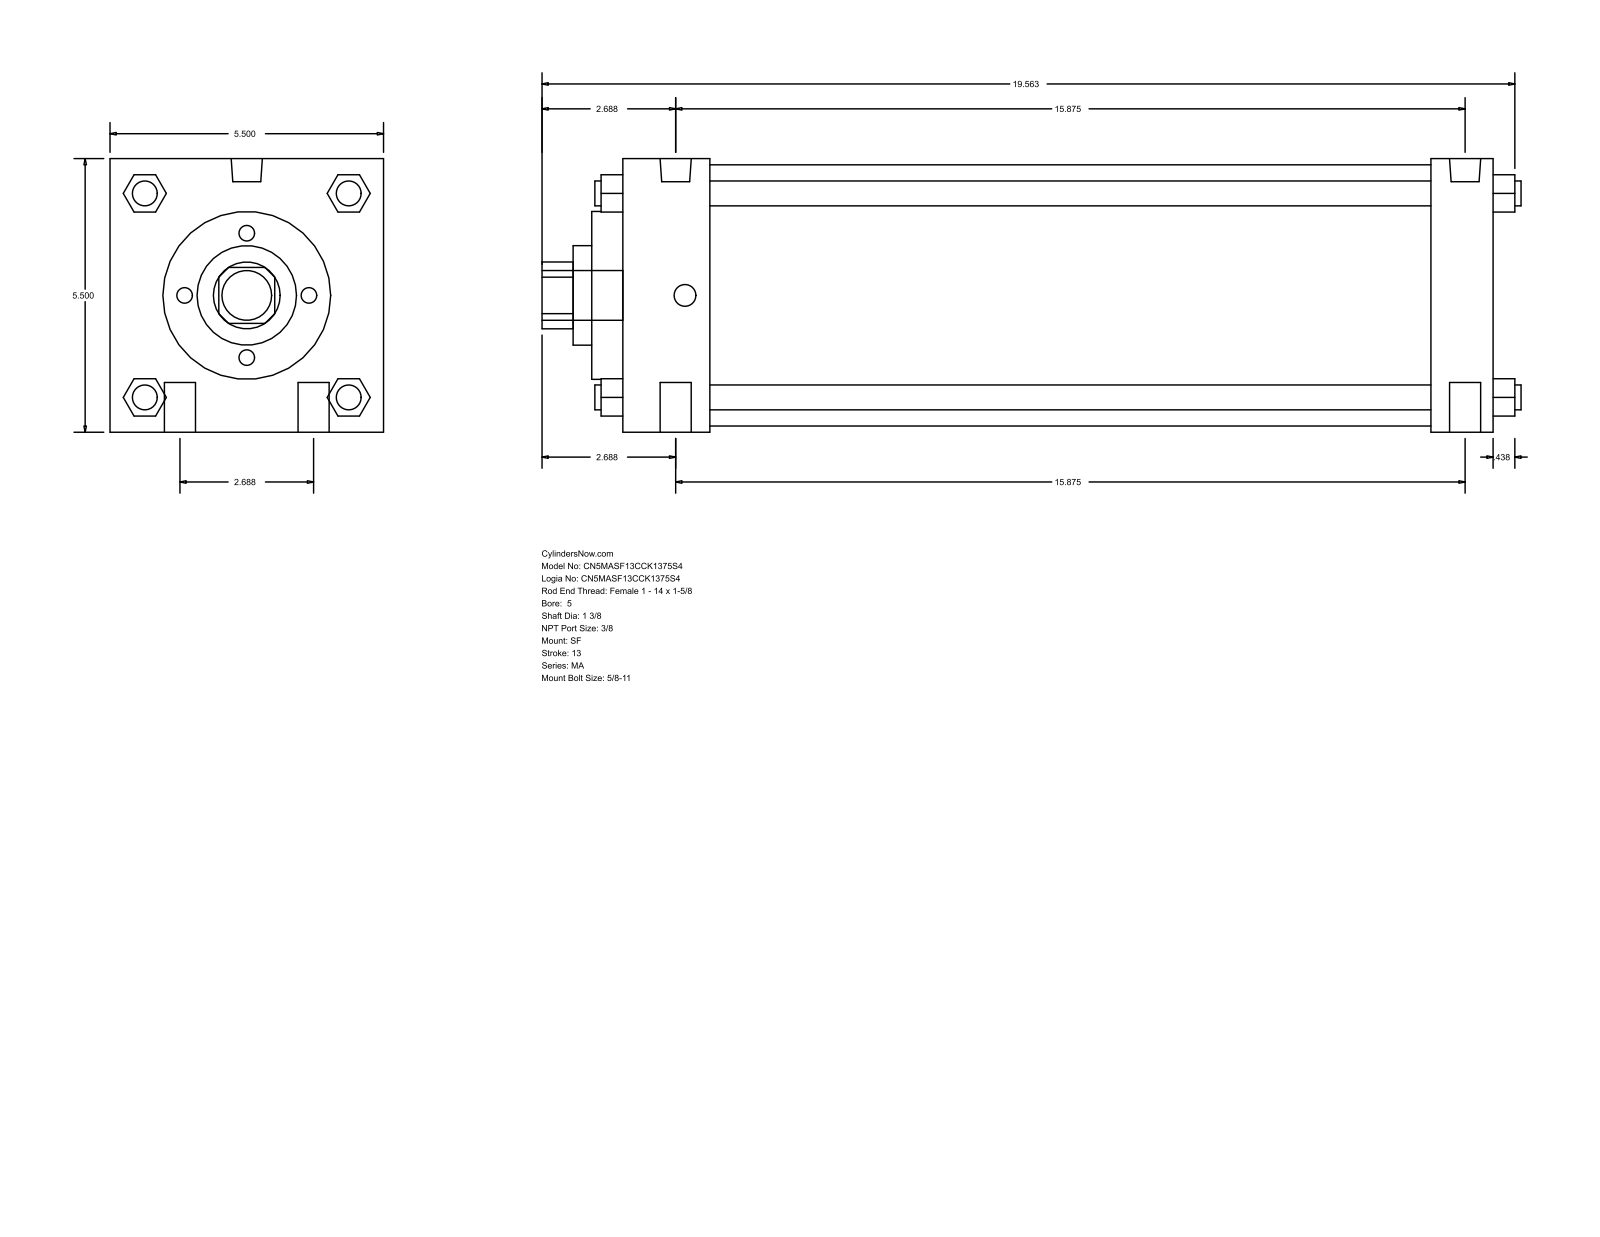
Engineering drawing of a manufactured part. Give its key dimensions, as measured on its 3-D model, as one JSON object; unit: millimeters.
{"part_name": "MA_SF__0500_1.375", "step_written_by": "GSSL Pune (CONFIG_CONTROL_DESIGN)", "units": "millimeters", "bodies": {"solids": 0, "faces": 126, "planar": 95, "cylindrical": 31, "other": 0}, "overall_size": [500.06, 139.7, 139.7], "round_holes": [[34.92, 1], [50.8, 1], [85.72, 1], [133.35, 1]], "round_bosses_or_shafts": [[15.88, 4], [12.7, 4], [15.93, 2], [11.11, 2], [25.4, 1]], "partial_cylinders_radius": [[17.06, 1]], "face_to_face_distances": [139.7, 444.5, 44.45, 412.75, 368.3, 400.05, 31.75, 15.87, 60.32, 428.62]}
